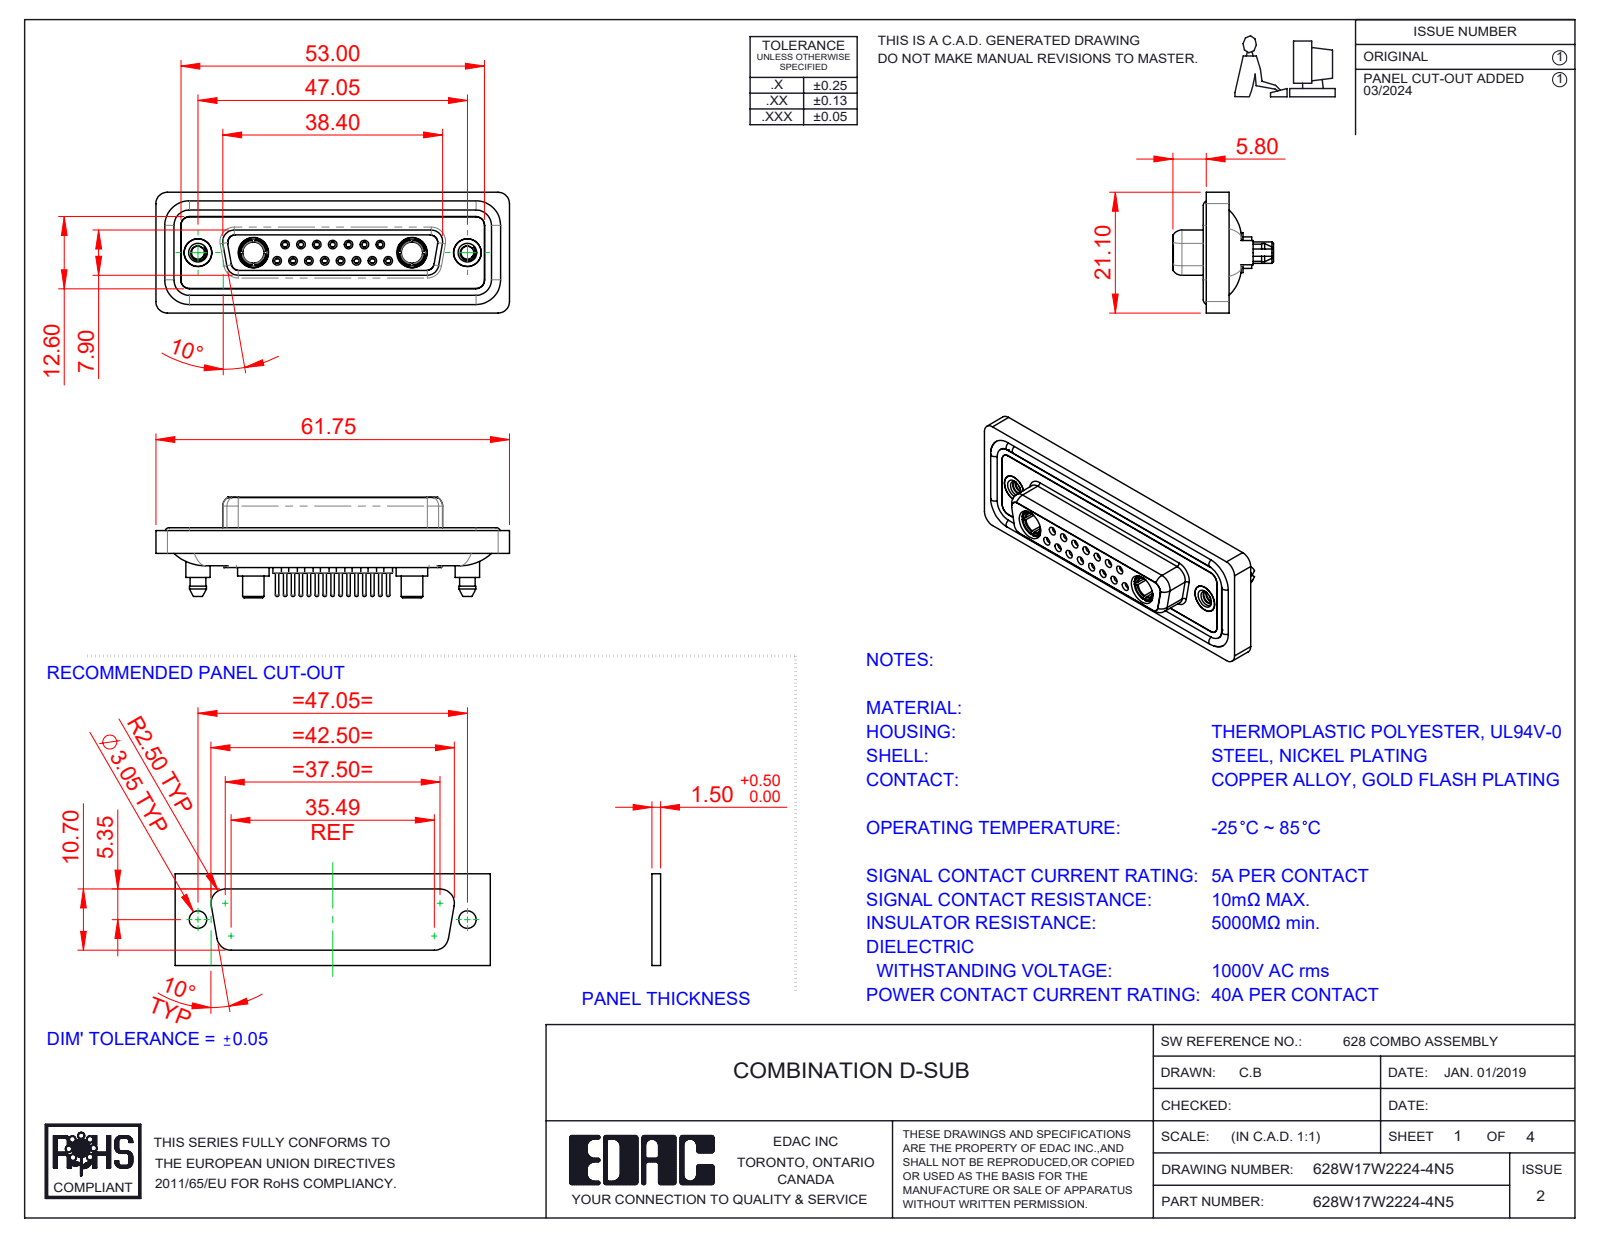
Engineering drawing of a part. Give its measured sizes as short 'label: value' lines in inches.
name: 628Combo Waterproof Housing_25 Contacts; 628Combo Contact Row 2_24; 628Combo Threaded Boardlock_5; 628Combo Housing_17W2 (+5 more)
written by: SolidWorks 2023 (CONFIG_CONTROL_DESIGN)
unit: in
bodies: 26 solids, 1409 faces (404 planar, 551 cylindrical, 454 other)
size: 2.431 × 0.831 × 0.691
volume: 0.518 in³; area: 22.03 in²
holes: 15× ⌀0.035, 15× ⌀0.043, 15× ⌀0.059, 15× ⌀0.079, 8× ⌀0.063, 7× ⌀0.067, 4× ⌀0.191, 2× ⌀0.089, 2× ⌀0.146, 2× ⌀0.157, 2× ⌀0.159, 2× ⌀0.197
bosses: 15× ⌀0.087, 15× ⌀0.024, 11× ⌀0.063, 2× ⌀0.217, 2× ⌀0.213, 2× ⌀0.205, 2× ⌀0.195, 2× ⌀0.195
rounds: 24× R0.059, 18× R0.079, 10× R0.063, 8× R0.053, 4× R0.01, 4× R0.02, 4× R0.024, 4× R0.026
face distances: 0.016, 0.071, 0.293, 0.222, 0.26, 0.02, 0.278, 0.063, 0.114, 0.043
hole spacings: 0.124, 0.109, 0.327, 0.218, 0.198, 0.198, 0.295, 0.436
